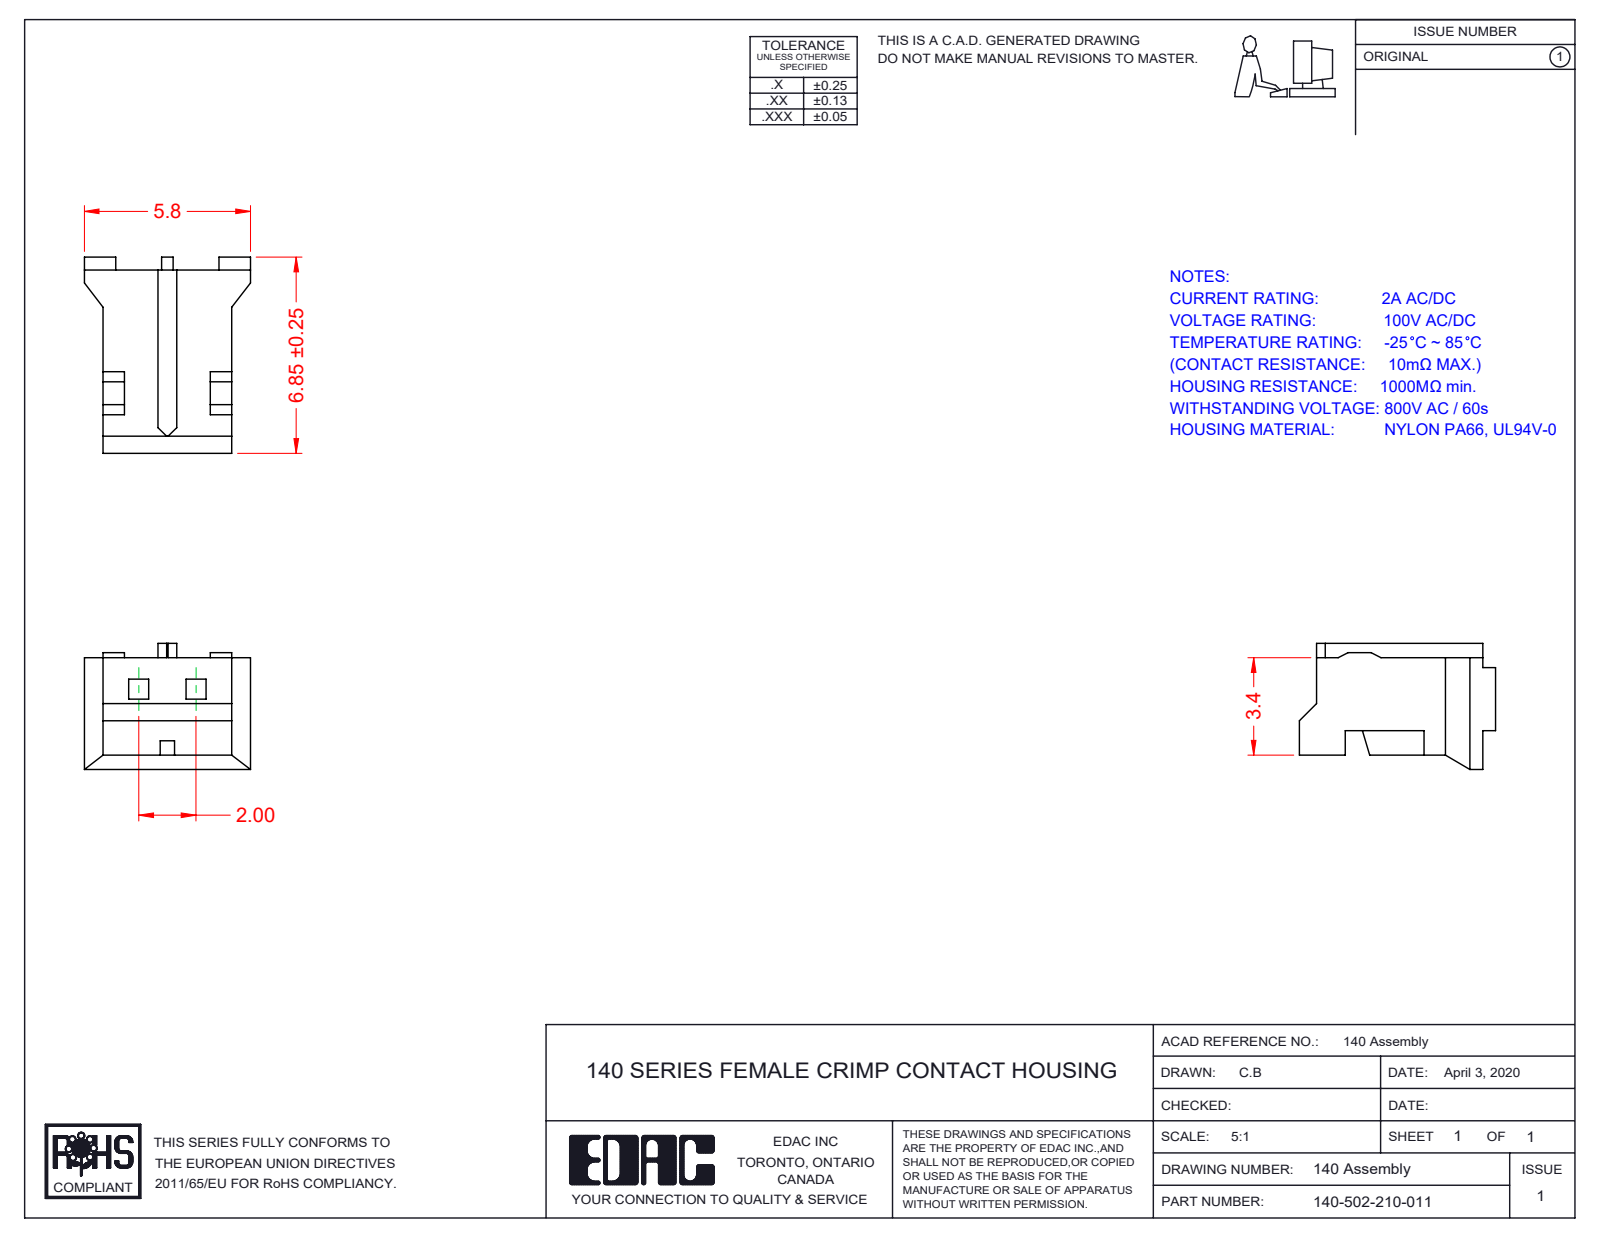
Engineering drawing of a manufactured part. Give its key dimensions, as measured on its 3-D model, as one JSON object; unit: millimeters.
{"part_name": "140-502-210-011", "step_written_by": "SolidWorks 2016 (CONFIG_CONTROL_DESIGN)", "units": "millimeters", "bodies": {"solids": 1, "faces": 88, "planar": 88, "cylindrical": 0, "other": 0}, "overall_size": [6.85, 5.8, 4.4], "volume_mm3": 57, "surface_area_mm2": 245, "face_to_face_distances": [0.45, 2, 2.05, 1.6, 2.45, 4.05, 0.85, 0.35, 2.55, 2.2]}
